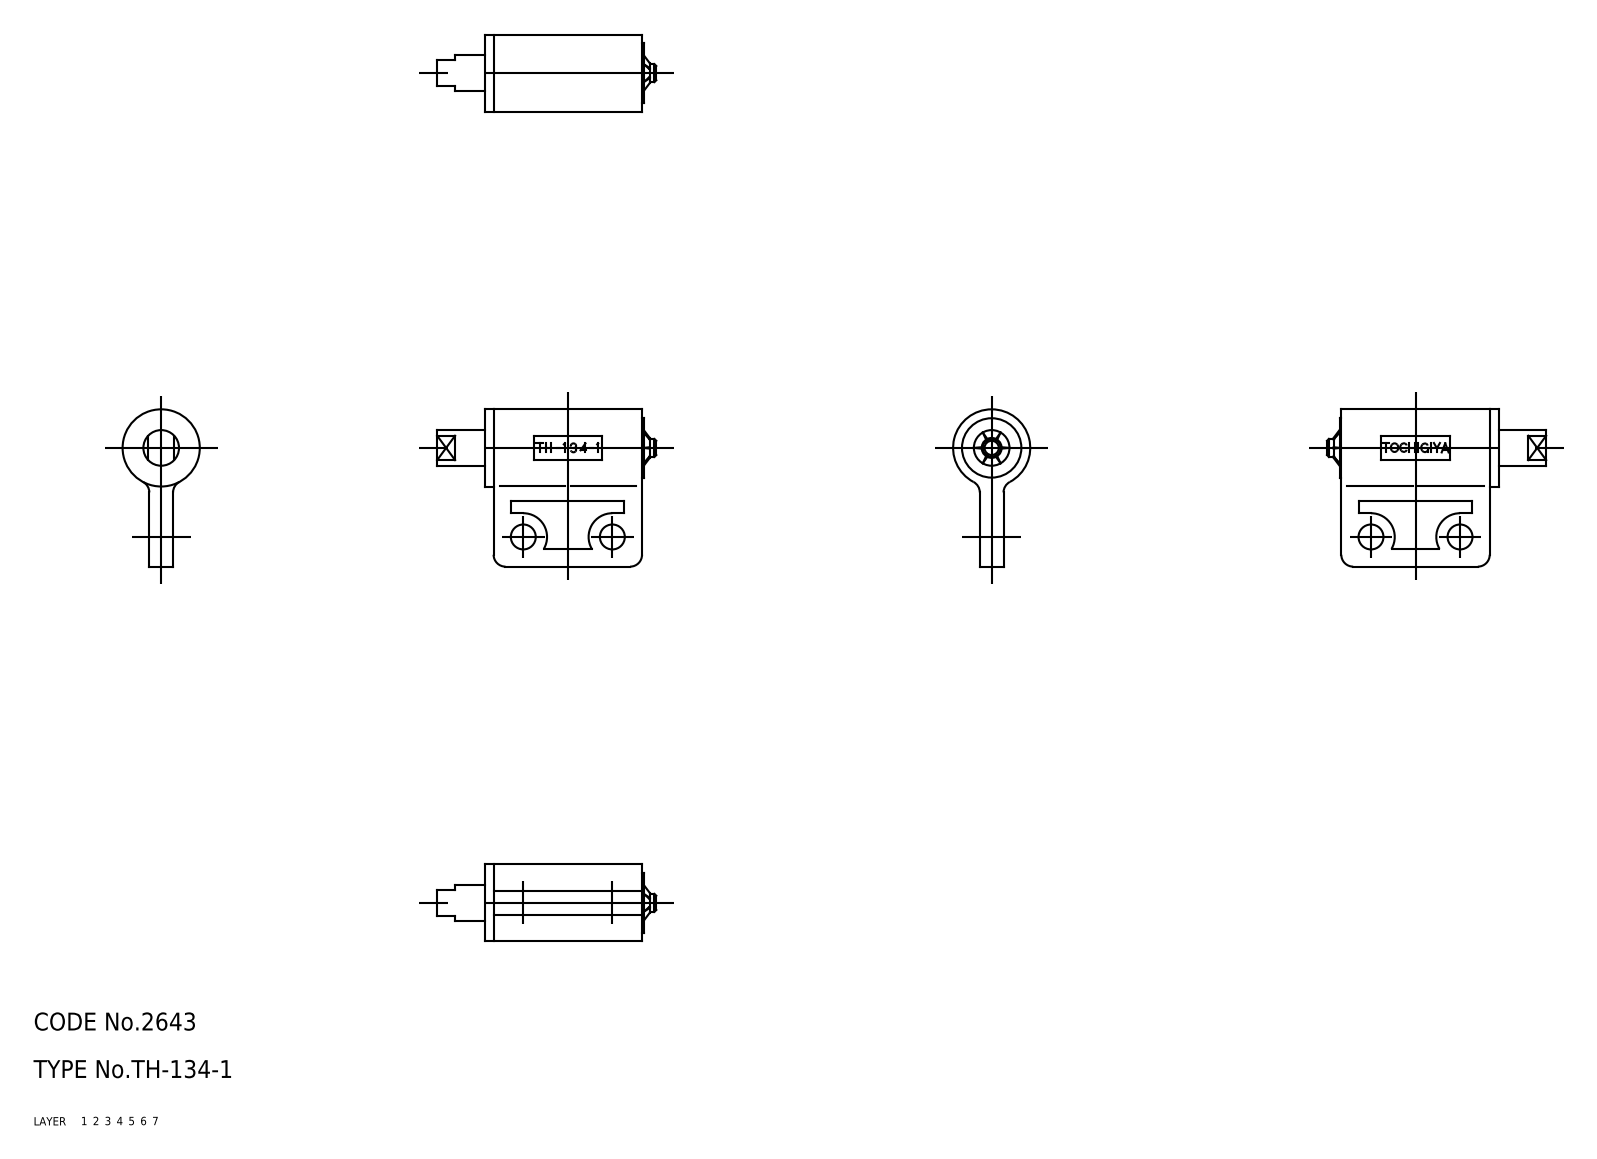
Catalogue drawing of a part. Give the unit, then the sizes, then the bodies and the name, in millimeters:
Units: millimetres
Overall size (bounding box): 36.9 × 26.5 × 13
Volume: 4 388 mm³ · Surface area: 3 823 mm²
Bodies: 3 solids, 101 faces (0 planar, 0 cylindrical, 101 other)
Part name (STEP PRODUCT): shaft; retainer; case; TH_134_1_3745_36
STEP written by: CADfix (AUTOMOTIVE_DESIGN)
